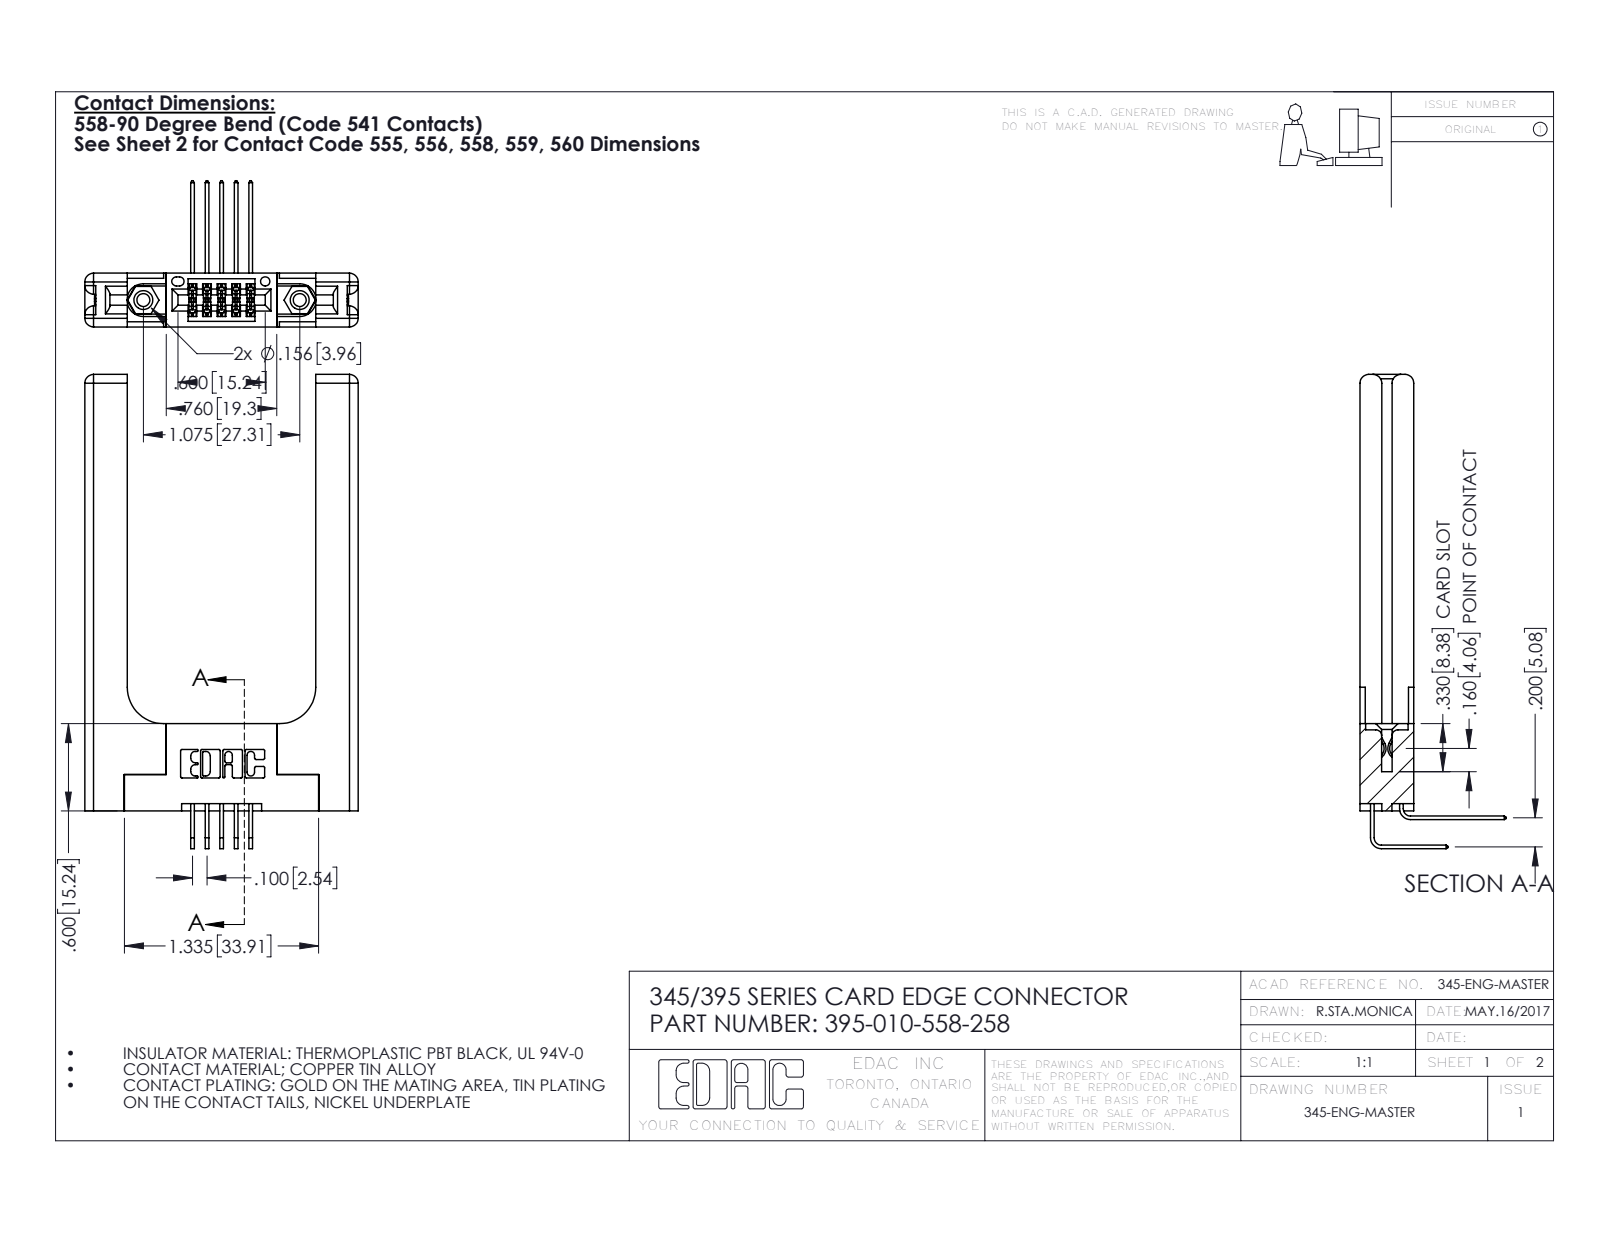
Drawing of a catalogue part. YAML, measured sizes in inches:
part_name: "395-010-558-258; 345-250-001_345-250-001-102; 345-292-001_558 559 Tail - 1; 345-220-058_345-220-058 (+2 more)"
step_written_by: "SolidWorks 2016 (CONFIG_CONTROL_DESIGN)"
units: inches
bodies: {solids: 15, faces: 902, planar: 578, cylindrical: 264, other: 60}
overall_size: [3.259, 1.879, 1.005]
volume: 0.783
surface_area: 17.12
round_holes:
  - {diameter: 0.089, count: 2}
  - {diameter: 0.125, count: 2}
  - {diameter: 0.156, count: 2}
  - {diameter: 0.064, count: 1}
round_bosses_or_shafts:
  - {diameter: 0.155, count: 2}
partial_cylinders:
  - {radius: 0.01, count: 22}
  - {radius: 0.006, count: 16}
  - {radius: 0.06, count: 16}
  - {radius: 0.007, count: 6}
  - {radius: 0.031, count: 6}
  - {radius: 0.026, count: 3}
  - {radius: 0.014, count: 2}
  - {radius: 0.019, count: 2}
face_to_face_distances: [0.37, 0.15, 0.22, 0.072, 1.296, 0.2, 0.077, 0.148, 0.298, 0.071]
hole_center_spacings: [0.27, 0.847, 1.075]
